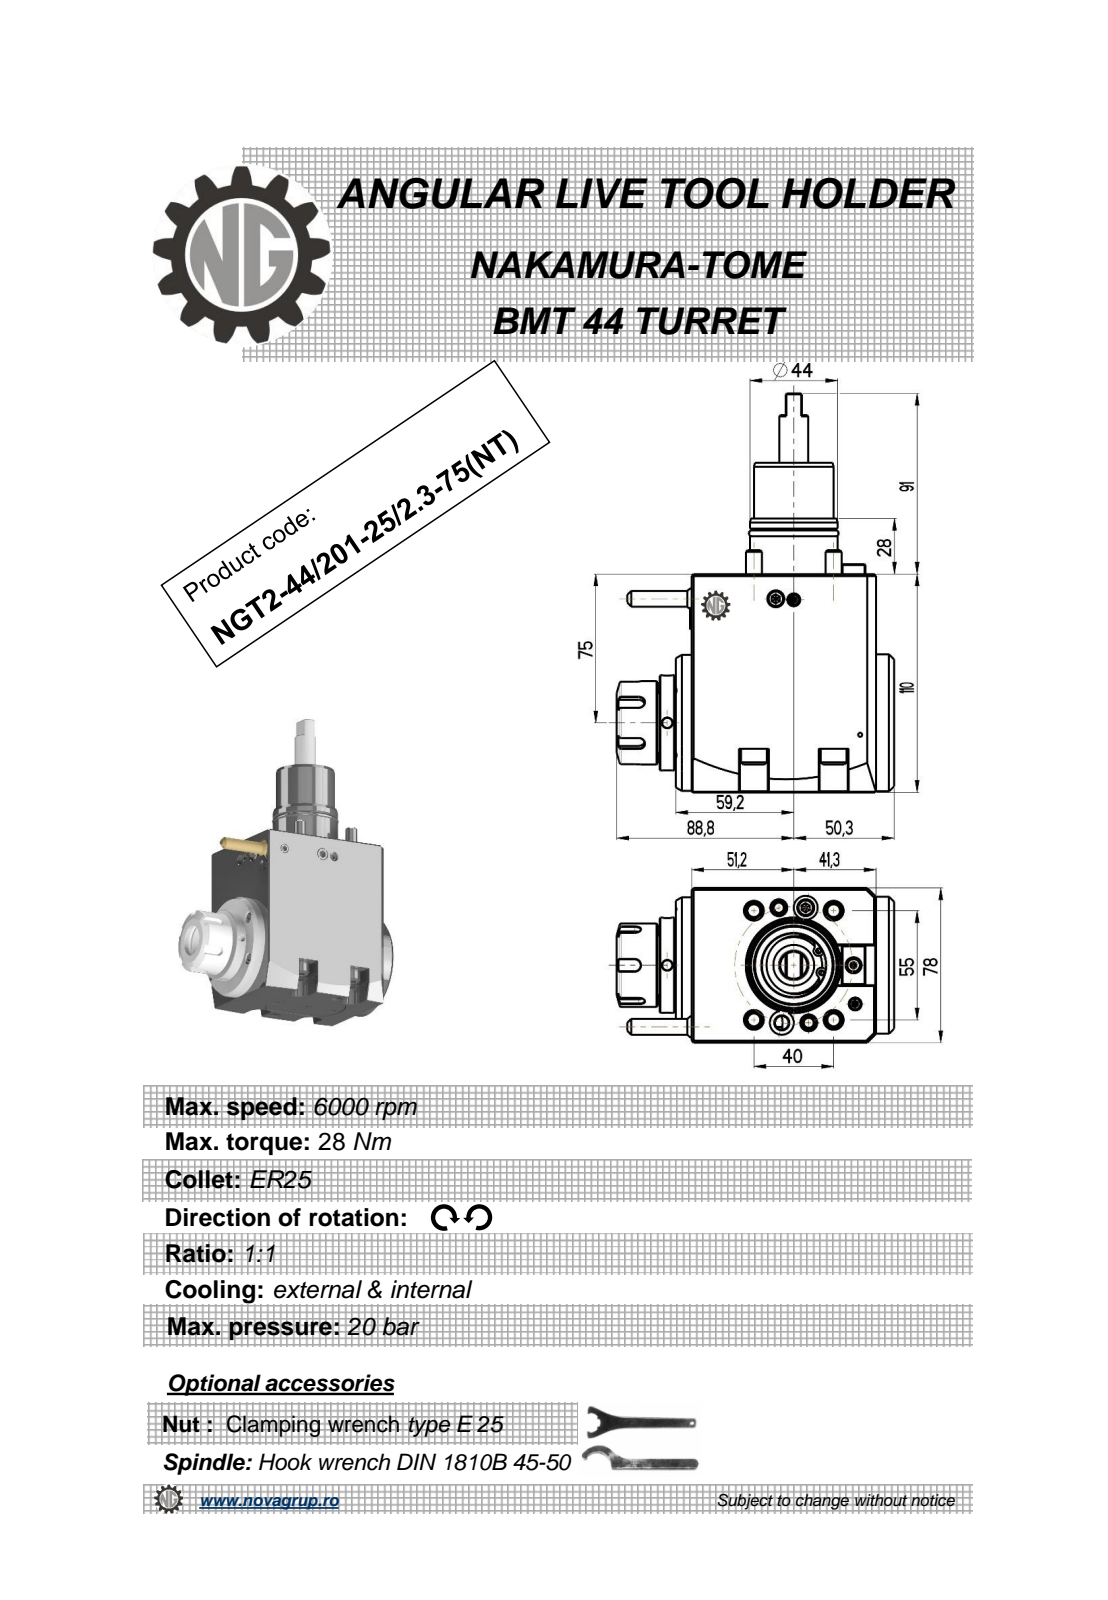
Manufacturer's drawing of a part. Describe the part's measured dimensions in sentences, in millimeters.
The part is named "NGT2_44_201_25_2_3_75_NT". Its 3-D file was written by "PRO/ENGINEER BY PARAMETRIC TECHNOLOGY CORPORATION, 2010280 (CONFIG_CONTROL_DESIGN)". It is 2 solids with 394 faces: 168 planar, 111 cylindrical and 115 other. Overall it measures 201 by 139.1 by 78 millimeters. Its volume is 960 071 cubic millimeters and its surface area 78 852 square millimeters. Round holes: 3 of diameter 5, 2 of diameter 6.8, 1 of diameter 3, 1 of diameter 20.3. Round bosses or shafts: 5 of diameter 8, 4 of diameter 13, 1 of diameter 69, 1 of diameter 68.5, 1 of diameter 48, 1 of diameter 44, 1 of diameter 42, 1 of diameter 40. Partial cylindrical surfaces (rounded edges, fillets, slot ends): 20 of radius 0.26, 6 of radius 0.22, 5 of radius 3, 4 of radius 7, 2 of radius 0.8, 2 of radius 390. The main face-to-face distances are 78, 110, 92.5, 9, 8, 101.5, 100.5, 109.5, 14, 56. The hole center spacings are 59.23, 64.35, 69.77, 75.26.
